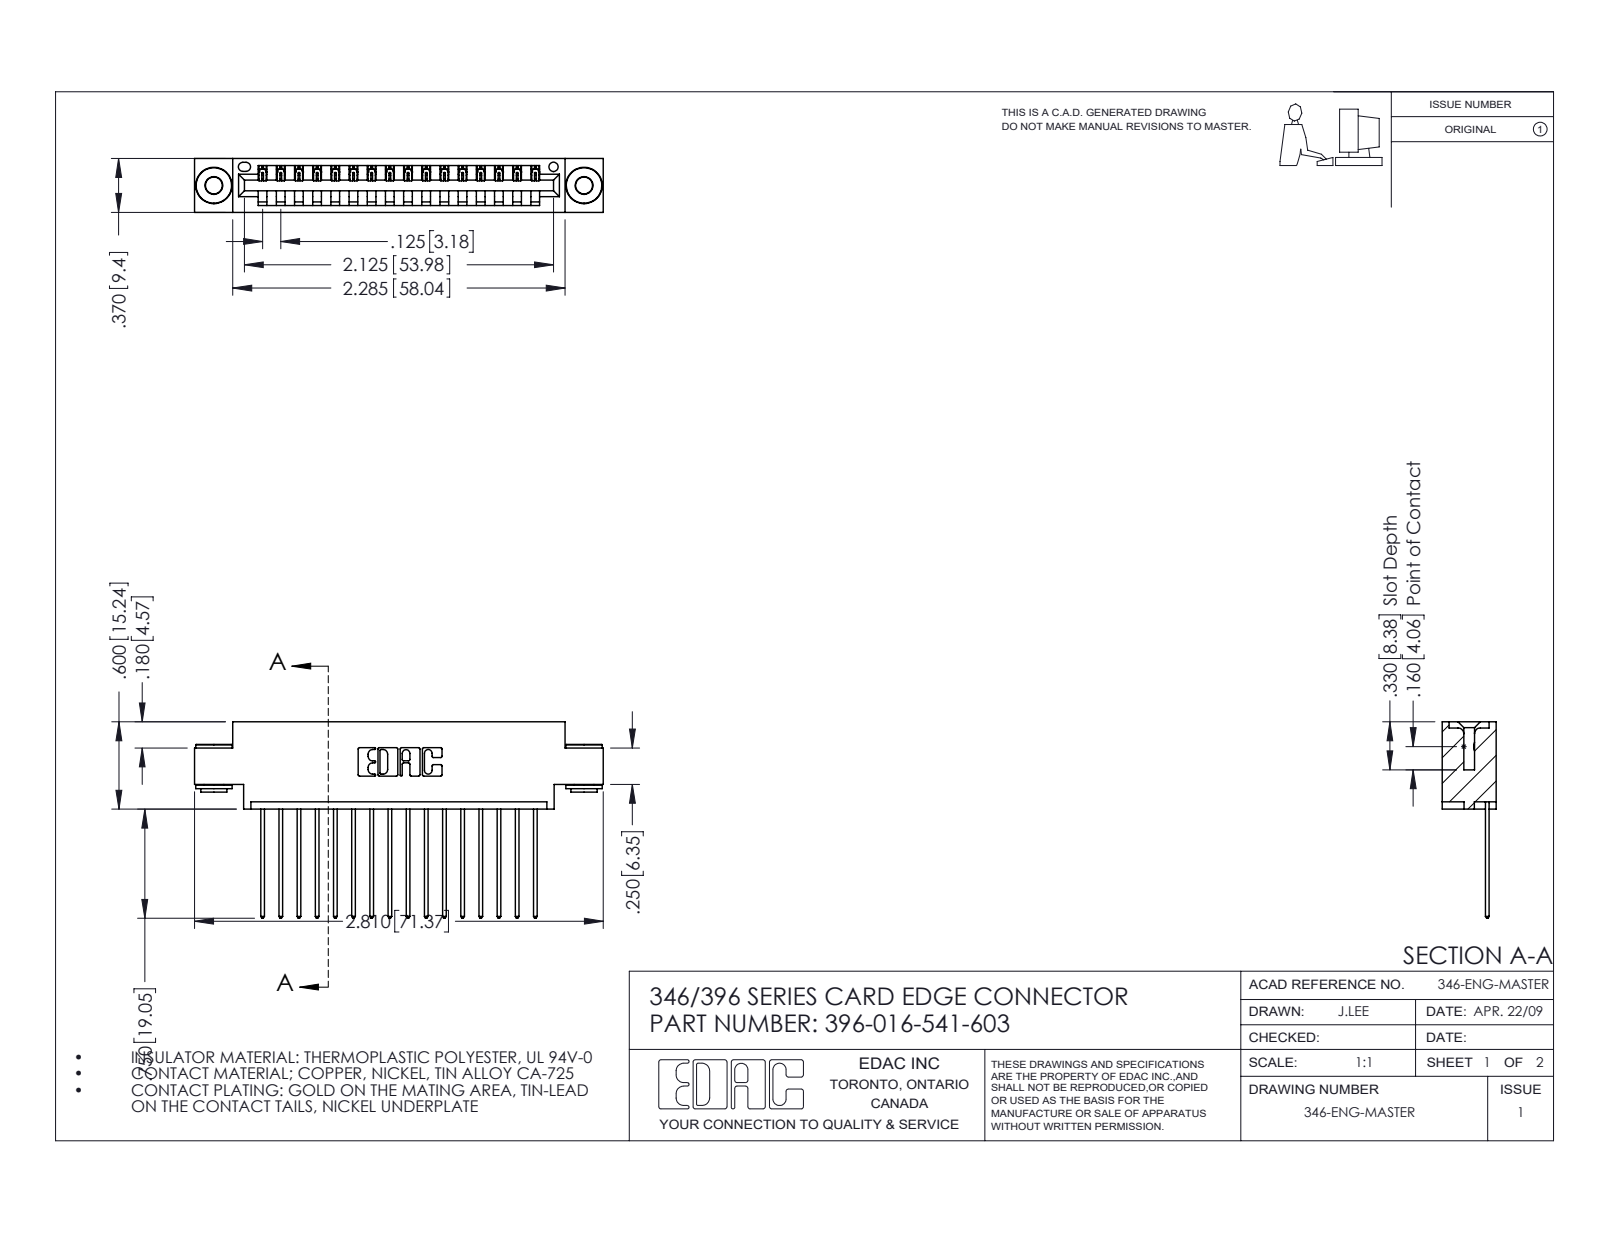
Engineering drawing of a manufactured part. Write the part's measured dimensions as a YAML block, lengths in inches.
part_name: "345-250-002_345-250-002-102; 346 Part_0.170 Offset - 0.156 Dia-TH; 345-292-001_345-293-141; 396-016-541-603"
step_written_by: "SolidWorks 2016 (CONFIG_CONTROL_DESIGN)"
units: inches
bodies: {solids: 19, faces: 1092, planar: 730, cylindrical: 354, other: 8}
overall_size: [2.81, 1.35, 0.37]
volume: 0.401
surface_area: 13.37
round_holes:
  - {diameter: 0.116, count: 2}
  - {diameter: 0.156, count: 2}
  - {diameter: 0.064, count: 1}
round_bosses_or_shafts:
  - {diameter: 0.25, count: 2}
  - {diameter: 0.18, count: 2}
  - {diameter: 0.136, count: 2}
partial_cylinders:
  - {radius: 0.006, count: 32}
  - {radius: 0.01, count: 32}
  - {radius: 0.01, count: 22}
  - {radius: 0.007, count: 6}
  - {radius: 0.031, count: 6}
  - {radius: 0.026, count: 3}
  - {radius: 0.031, count: 2}
  - {radius: 0.04, count: 2}
face_to_face_distances: [0.048, 0.322, 0.37, 0.25, 0.025, 0.072, 0.298, 0.148, 0.222, 0.1]
hole_center_spacings: [0.246, 2.338, 2.545]
